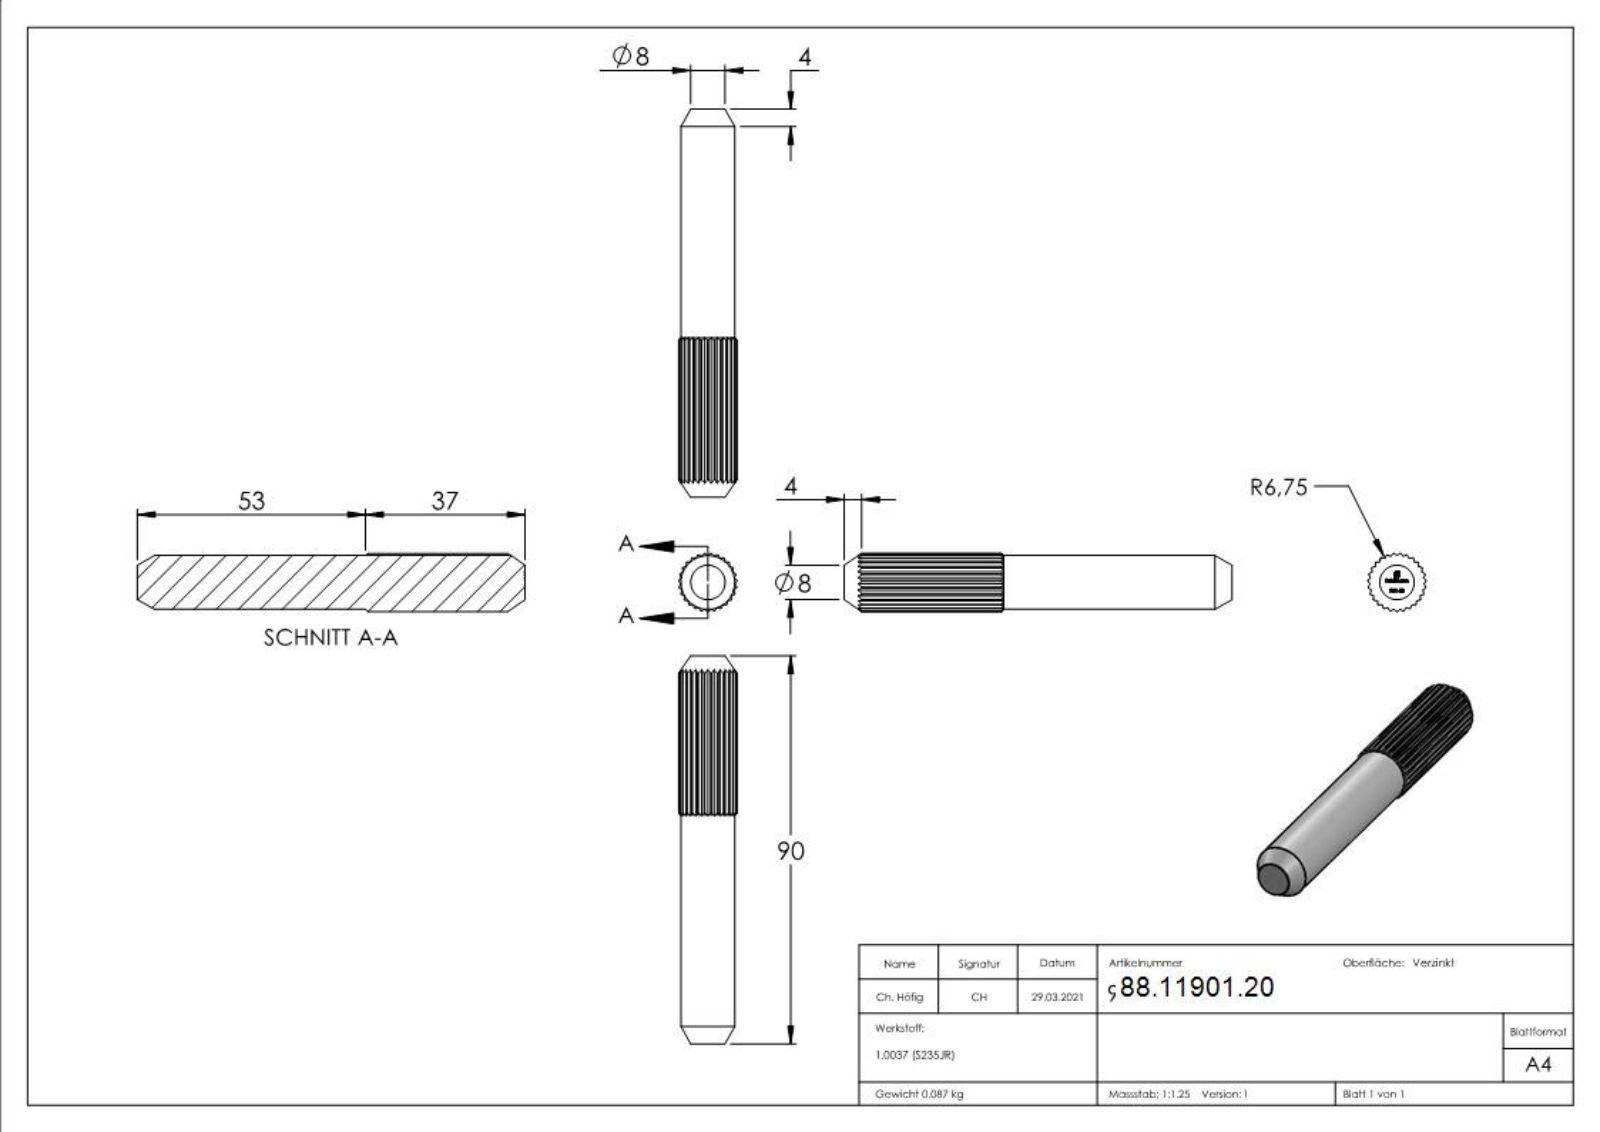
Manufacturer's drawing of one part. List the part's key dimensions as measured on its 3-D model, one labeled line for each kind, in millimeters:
Part name (STEP PRODUCT): 901-20
STEP written by: SolidWorks 2018 (CONFIG_CONTROL_DESIGN)
Units: millimetres
Bodies: 1 solid, 332 faces (170 planar, 29 cylindrical, 133 other)
Overall size (bounding box): 90 × 13.49 × 13.47
Volume: 11 135 mm³ · Surface area: 4 004 mm²
Round bosses / shafts (diameter × count): ⌀12.5 ×1
Partial cylindrical surfaces — rounded edges, fillets, slot ends (radius × count): R6.75 ×1
Main face-to-face distances: 90, 89.9, 0.79, 0.86, 0.99, 0.83, 1.15, 0.76, 1.12, 1.78
